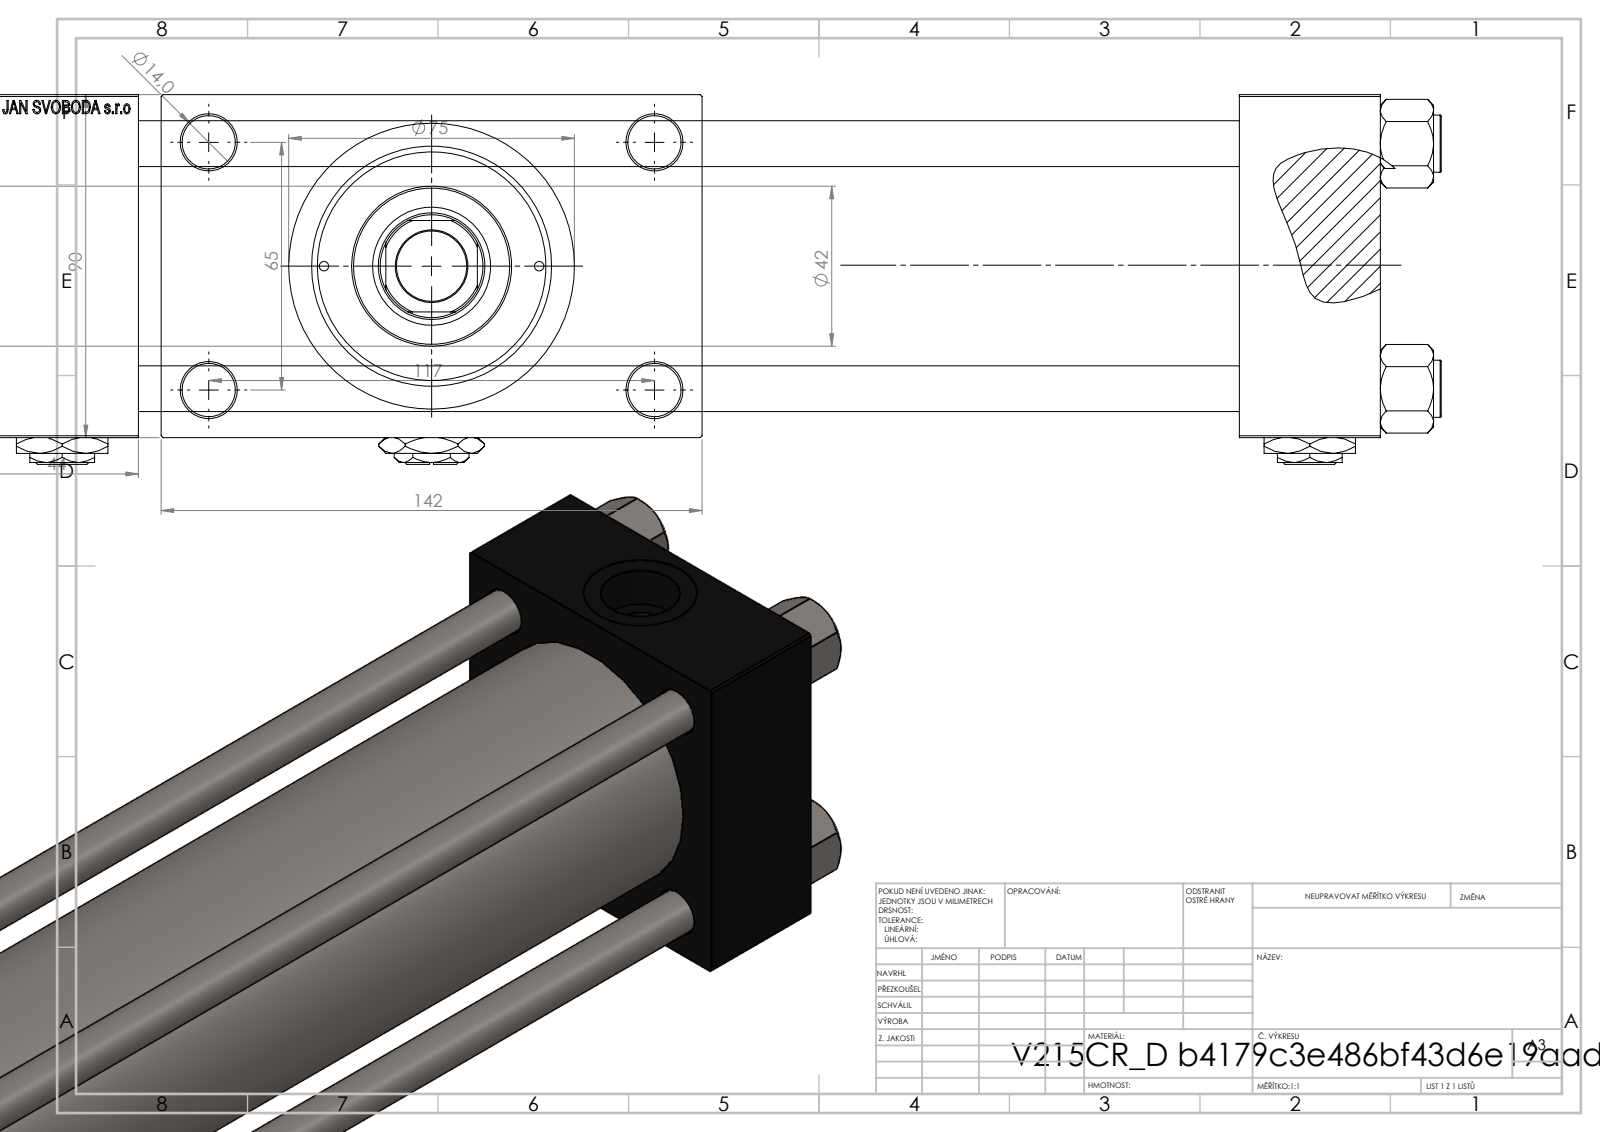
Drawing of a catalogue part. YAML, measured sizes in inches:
part_name: "V215CR_VCP_D; NUT_M5_D; V215CR_D_TYCINKA; V215CR_D_Body (+2 more)"
step_written_by: "SolidWorks 2019 (CONFIG_CONTROL_DESIGN)"
units: inches
bodies: {solids: 13, faces: 1213, planar: 547, cylindrical: 104, other: 562}
overall_size: [17.047, 5.591, 3.819]
volume: 90.8
surface_area: 547.8
round_holes:
  - {diameter: 0.472, count: 4}
  - {diameter: 0.551, count: 4}
  - {diameter: 0.098, count: 2}
  - {diameter: 0.276, count: 2}
  - {diameter: 0.825, count: 2}
  - {diameter: 1.181, count: 2}
  - {diameter: 0.728, count: 1}
  - {diameter: 1.102, count: 1}
  - {diameter: 1.22, count: 1}
  - {diameter: 1.969, count: 1}
  - {diameter: 2.362, count: 1}
  - {diameter: 2.48, count: 1}
round_bosses_or_shafts:
  - {diameter: 0.591, count: 4}
  - {diameter: 2.953, count: 1}
  - {diameter: 2.717, count: 1}
  - {diameter: 1.654, count: 1}
partial_cylinders:
  - {radius: 0.531, count: 1}
face_to_face_distances: [3.543, 11.378, 1.457, 12.835, 13.11, 14.567, 1.732, 1.024, 4.567, 5.591]
hole_center_spacings: [1.037, 1.275, 1.748, 1.79, 2.531, 2.635, 2.694, 2.748]
